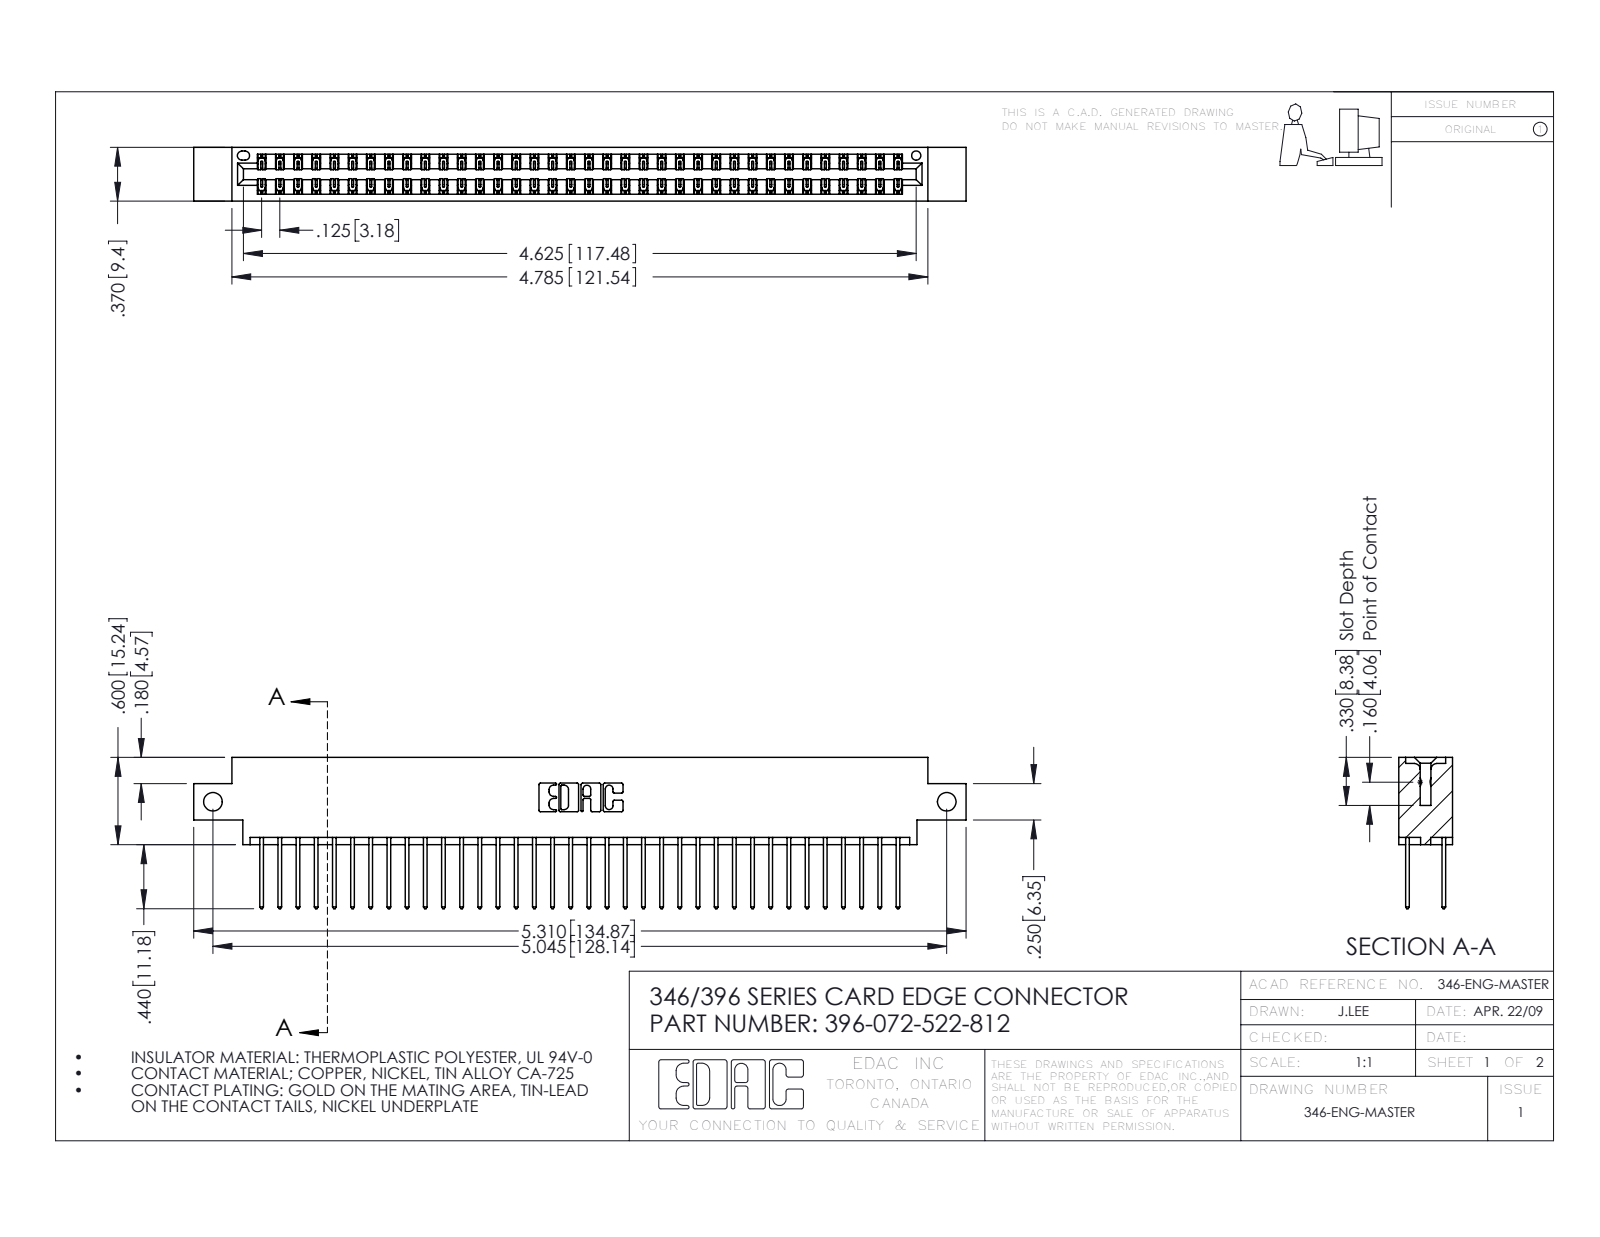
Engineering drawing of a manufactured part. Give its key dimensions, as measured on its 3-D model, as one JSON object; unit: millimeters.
{"part_name": "346 Part_0.170 Offset - Side Mount; 396-072-522-812; 345-292-001_345-293-122", "step_written_by": "SolidWorks 2016 (CONFIG_CONTROL_DESIGN)", "units": "millimeters", "bodies": {"solids": 73, "faces": 3870, "planar": 2600, "cylindrical": 1270, "other": 0}, "overall_size": [134.9, 26.4, 9.4], "volume_mm3": 13000, "surface_area_mm2": 18740, "round_holes": [[3.3, 2], [1.6, 1]], "partial_cylinders_radius": [[0.2, 108], [0.3, 72], [0.3, 22], [0.2, 6], [0.8, 6], [0.7, 3], [0.4, 2], [0.6, 2]], "face_to_face_distances": [1.2, 8.2, 6.4, 9.4, 1.8, 7.6, 0.6, 7, 3.8, 5.6], "hole_center_spacings": [128.1]}
